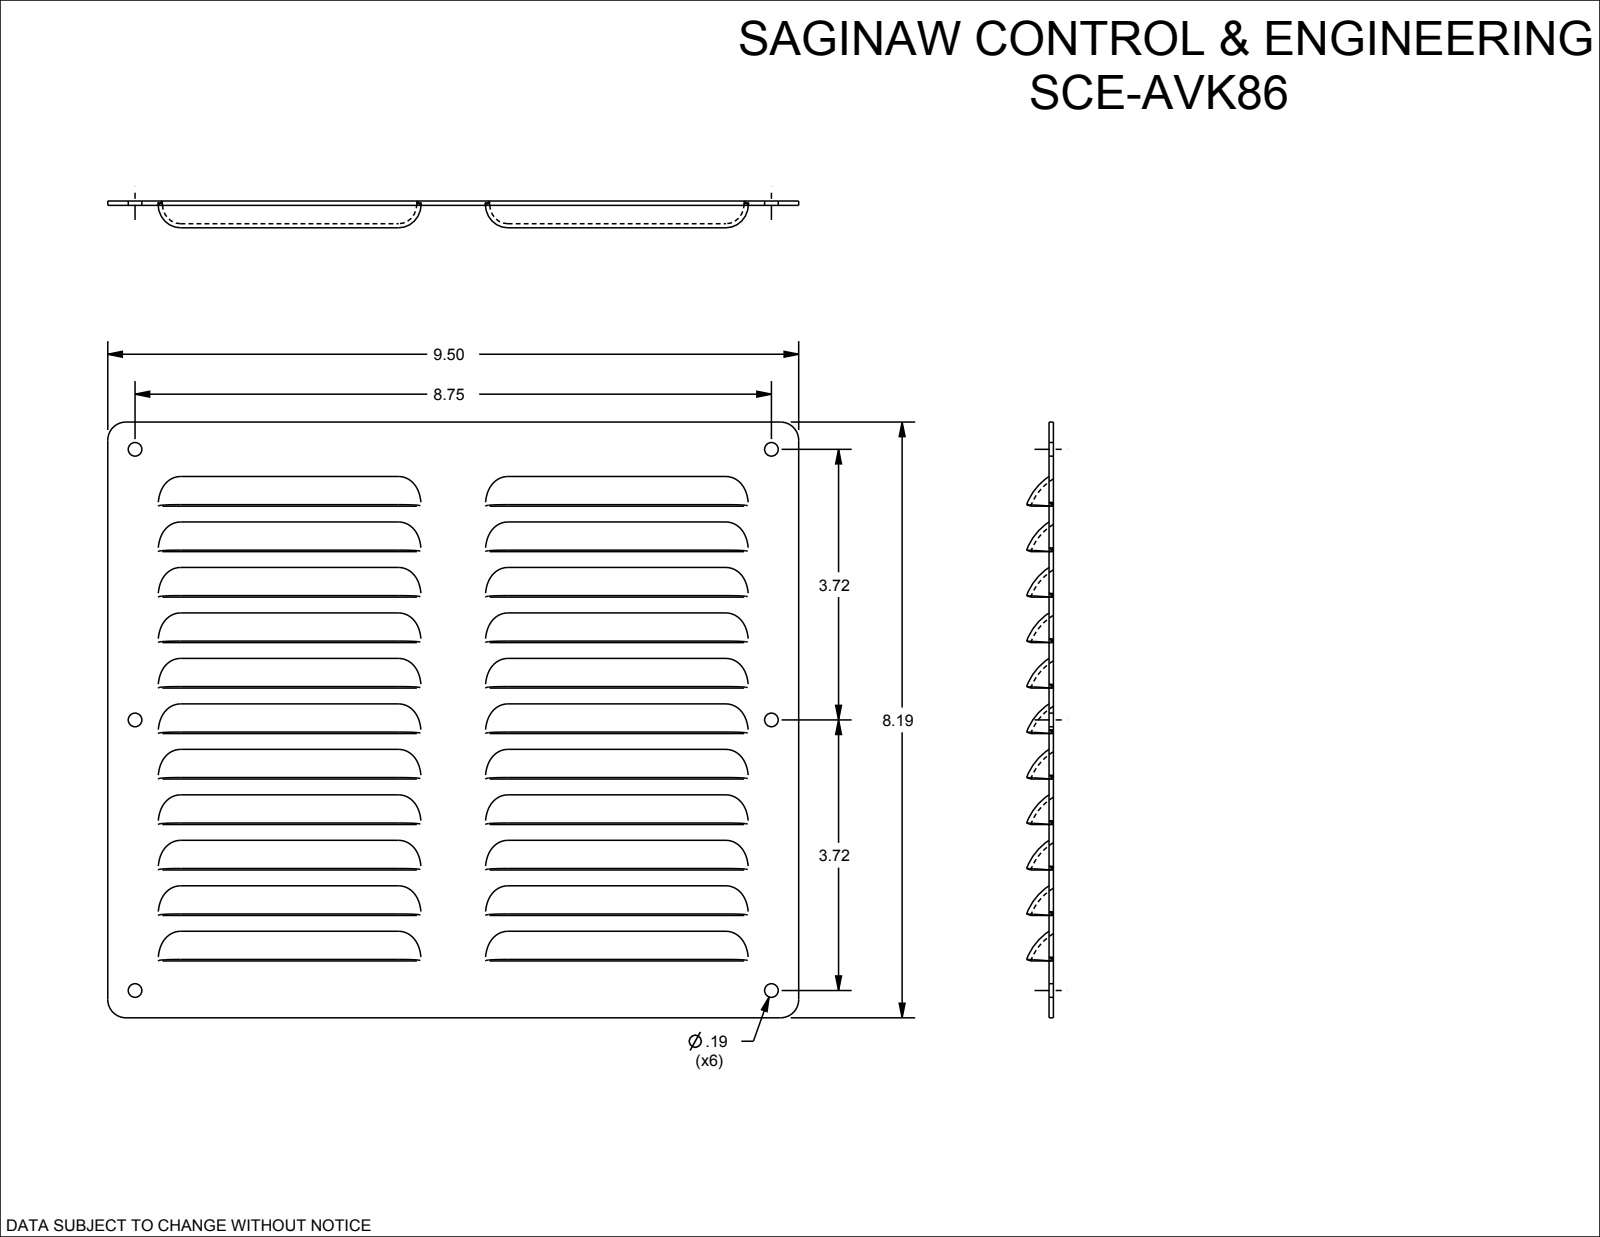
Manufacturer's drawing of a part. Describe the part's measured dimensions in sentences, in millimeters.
The part is named "SCE-AVK86". Its 3-D file was written by "SolidWorks 2021 (AUTOMOTIVE_DESIGN)". It is 1 solid with 352 faces: 72 planar, 104 cylindrical and 176 other. Overall it measures 241.3 by 208 by 11.9 millimeters. Its volume is 87 380 cubic millimeters and its surface area 121 700 square millimeters. Round holes: 6 of diameter 4.7. Partial cylindrical surfaces (rounded edges, fillets, slot ends): 11 of radius 18.8, 11 of radius 20.3, 4 of radius 6.4. The main face-to-face distances are 1.5, 31.8, 63.5, 29.7, 15.9, 95.3, 15.9, 24.4, 14.9, 59.5. The hole center spacings are 94.5, 241.5, 222.3, 188.9, 291.7.
